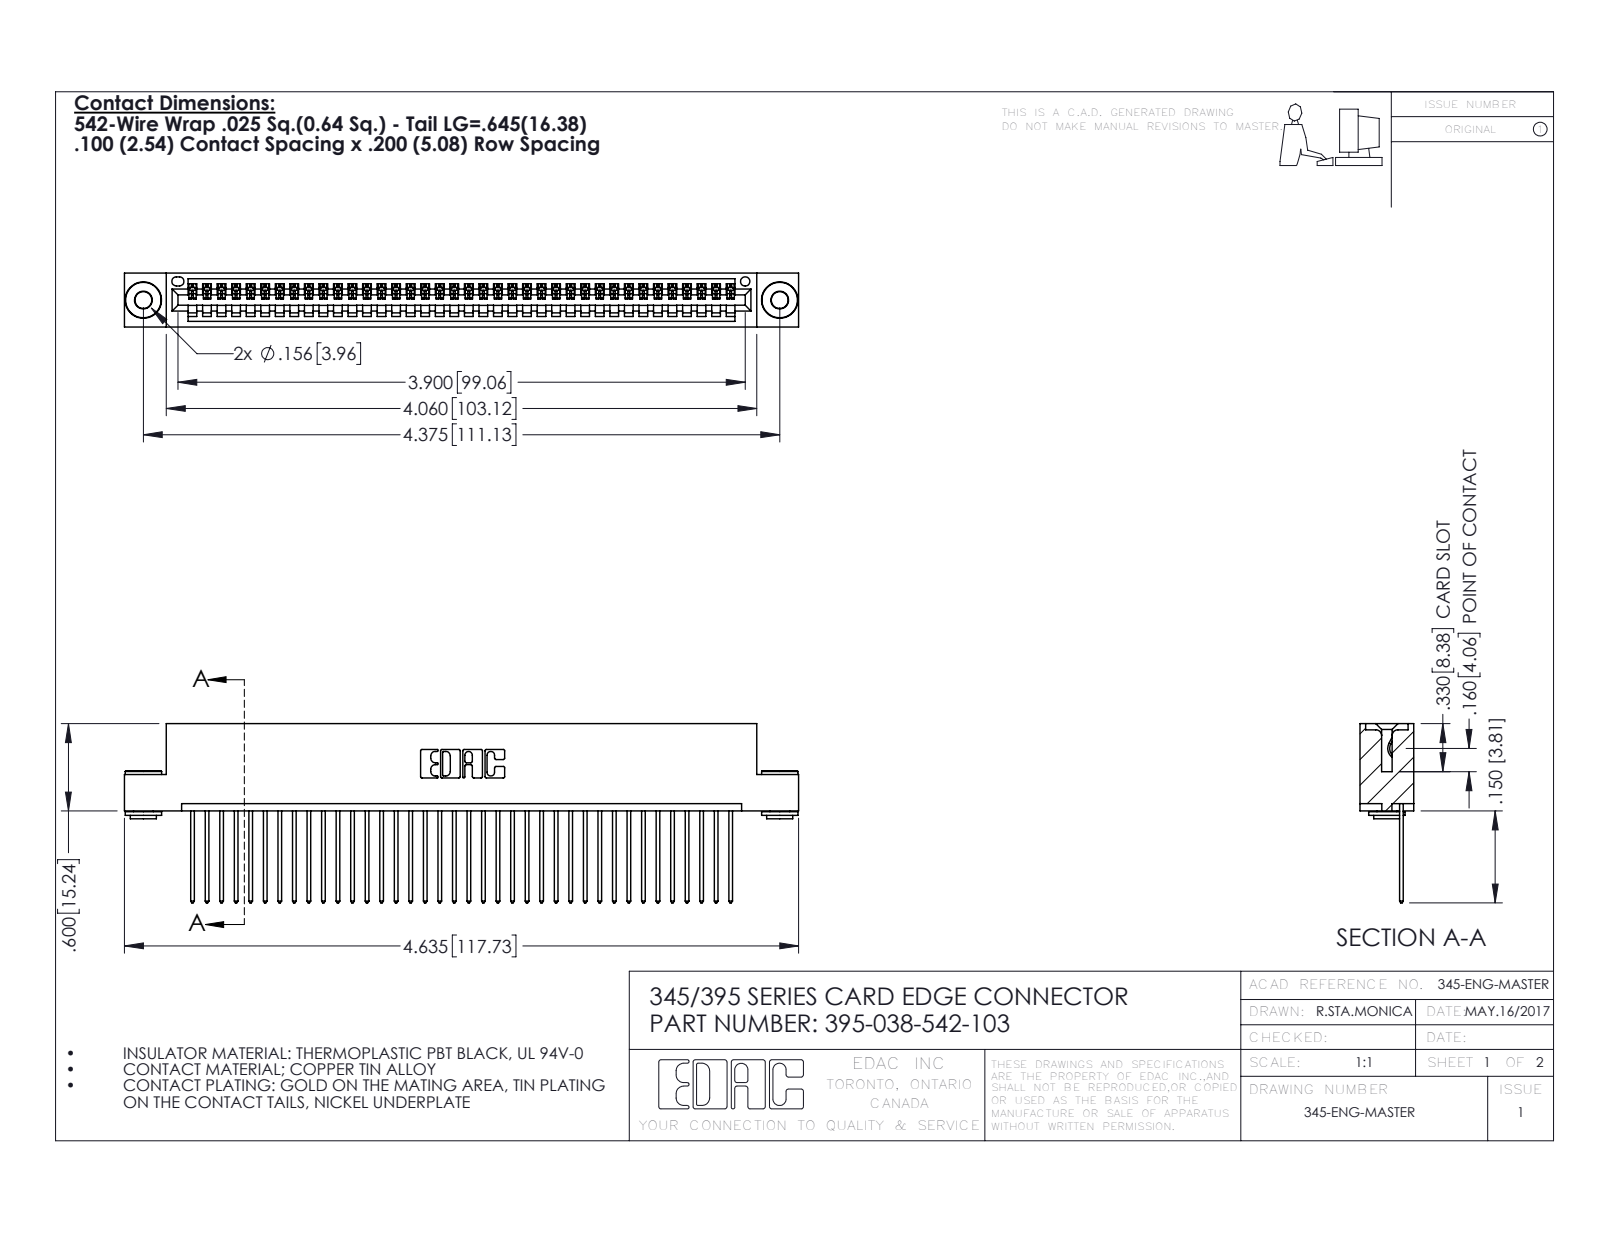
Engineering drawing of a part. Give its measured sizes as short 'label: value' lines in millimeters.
name: 395-038-542-103; 345-292-001_345-293-142; 345-250-002_345-250-002-102; 345 Part_Flush Mounting Lugs - 0.156 Dia-TH
written by: SolidWorks 2016 (CONFIG_CONTROL_DESIGN)
unit: mm
bodies: 41 solids, 2368 faces (1610 planar, 750 cylindrical, 8 other)
size: 117.7 × 31.3 × 9.4
volume: 11 300 mm³; area: 15 650 mm²
holes: 2× ⌀2.9, 2× ⌀4, 1× ⌀1.6
bosses: 2× ⌀6.4, 2× ⌀4.6, 2× ⌀3.5
rounds: 76× R0.2, 76× R0.3, 22× R0.3, 6× R0.2, 6× R0.8, 3× R0.7, 2× R0.8, 2× R1
face distances: 1.8, 7.6, 5.1, 0.6, 9.4, 2.5, 6.9, 5.7, 3.8, 1.8
hole spacings: 6.9, 105.1, 111.1
